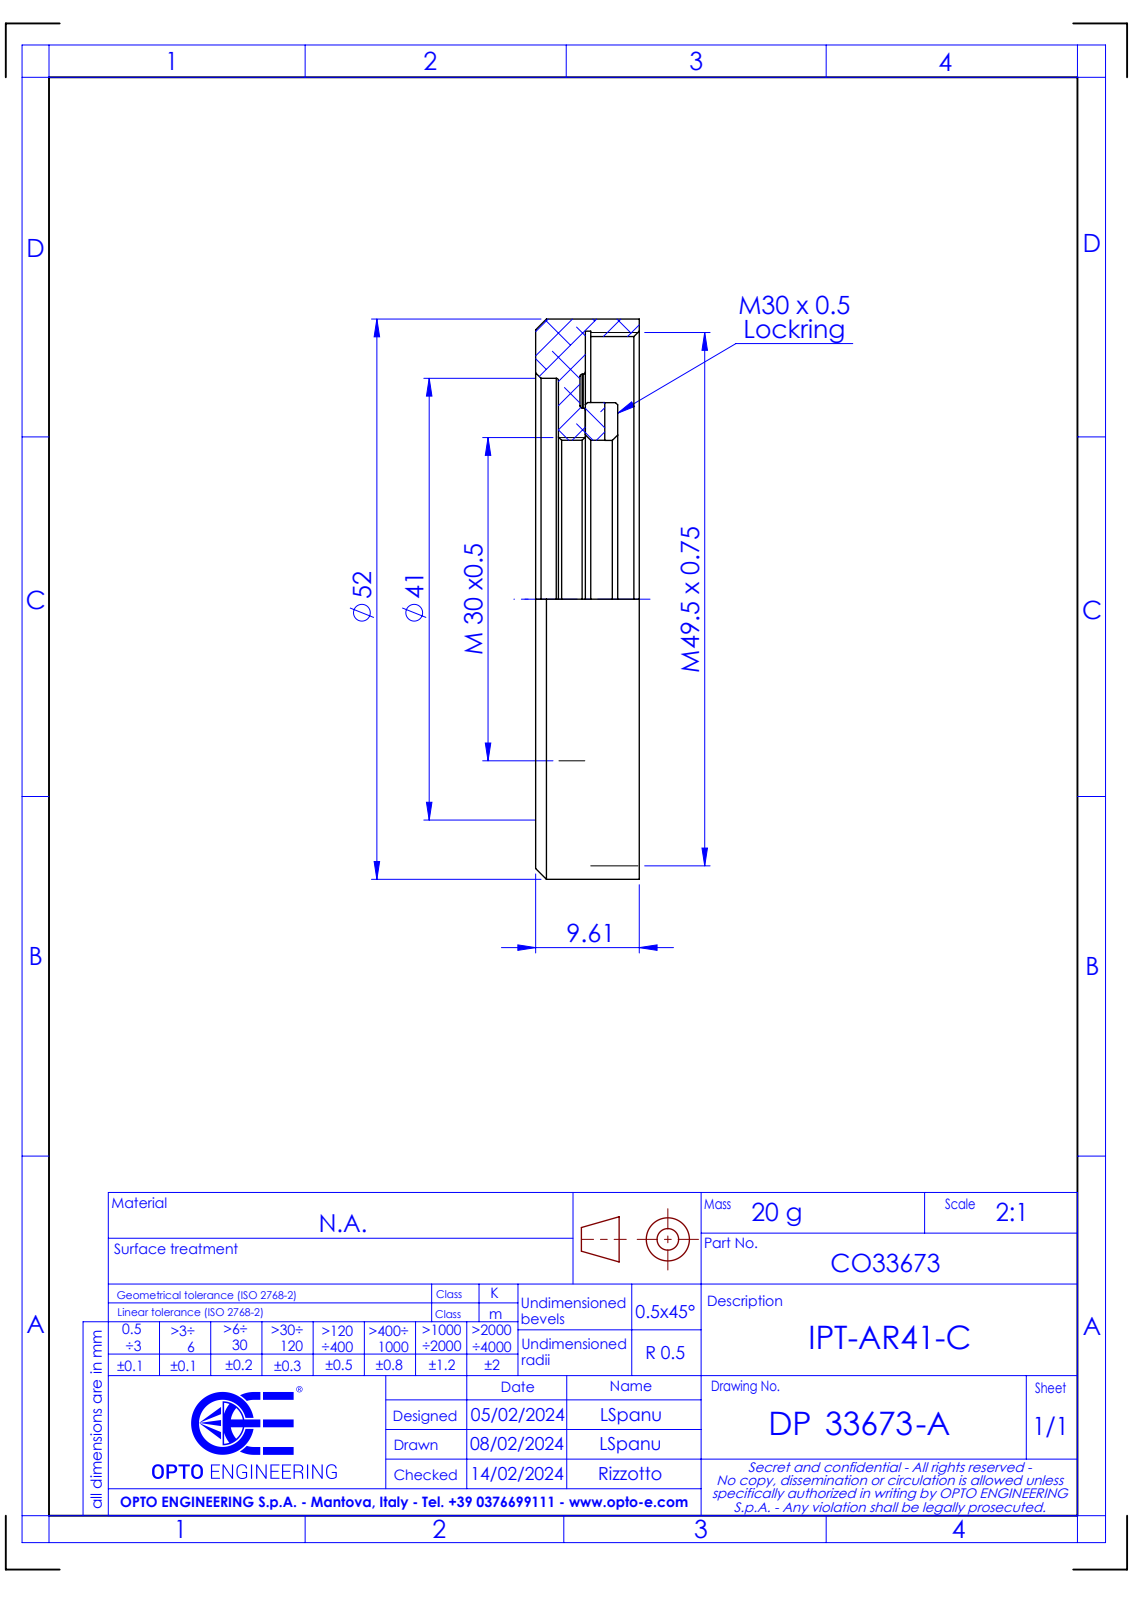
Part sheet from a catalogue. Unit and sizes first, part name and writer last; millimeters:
Units: millimetres
Overall size (bounding box): 52 × 52 × 9.61
Round holes (diameter × count): ⌀29.5 ×1, ⌀41 ×1, ⌀41.75 ×1, ⌀48.75 ×1, ⌀49.75 ×1
Round bosses / shafts (diameter × count): ⌀52 ×1, ⌀36.5 ×1, ⌀35.5 ×1
Main face-to-face distances: 2.5, 2.11, 4.61, 2, 5.5, 4.11, 0.5, 7.61, 3.5, 3
Bodies: 0 solids, 58 faces (14 planar, 18 cylindrical, 26 other)
Part name (STEP PRODUCT): DP33673-A_IPT-AR41-C
STEP written by: SolidWorks 2021 (CONFIG_CONTROL_DESIGN)
